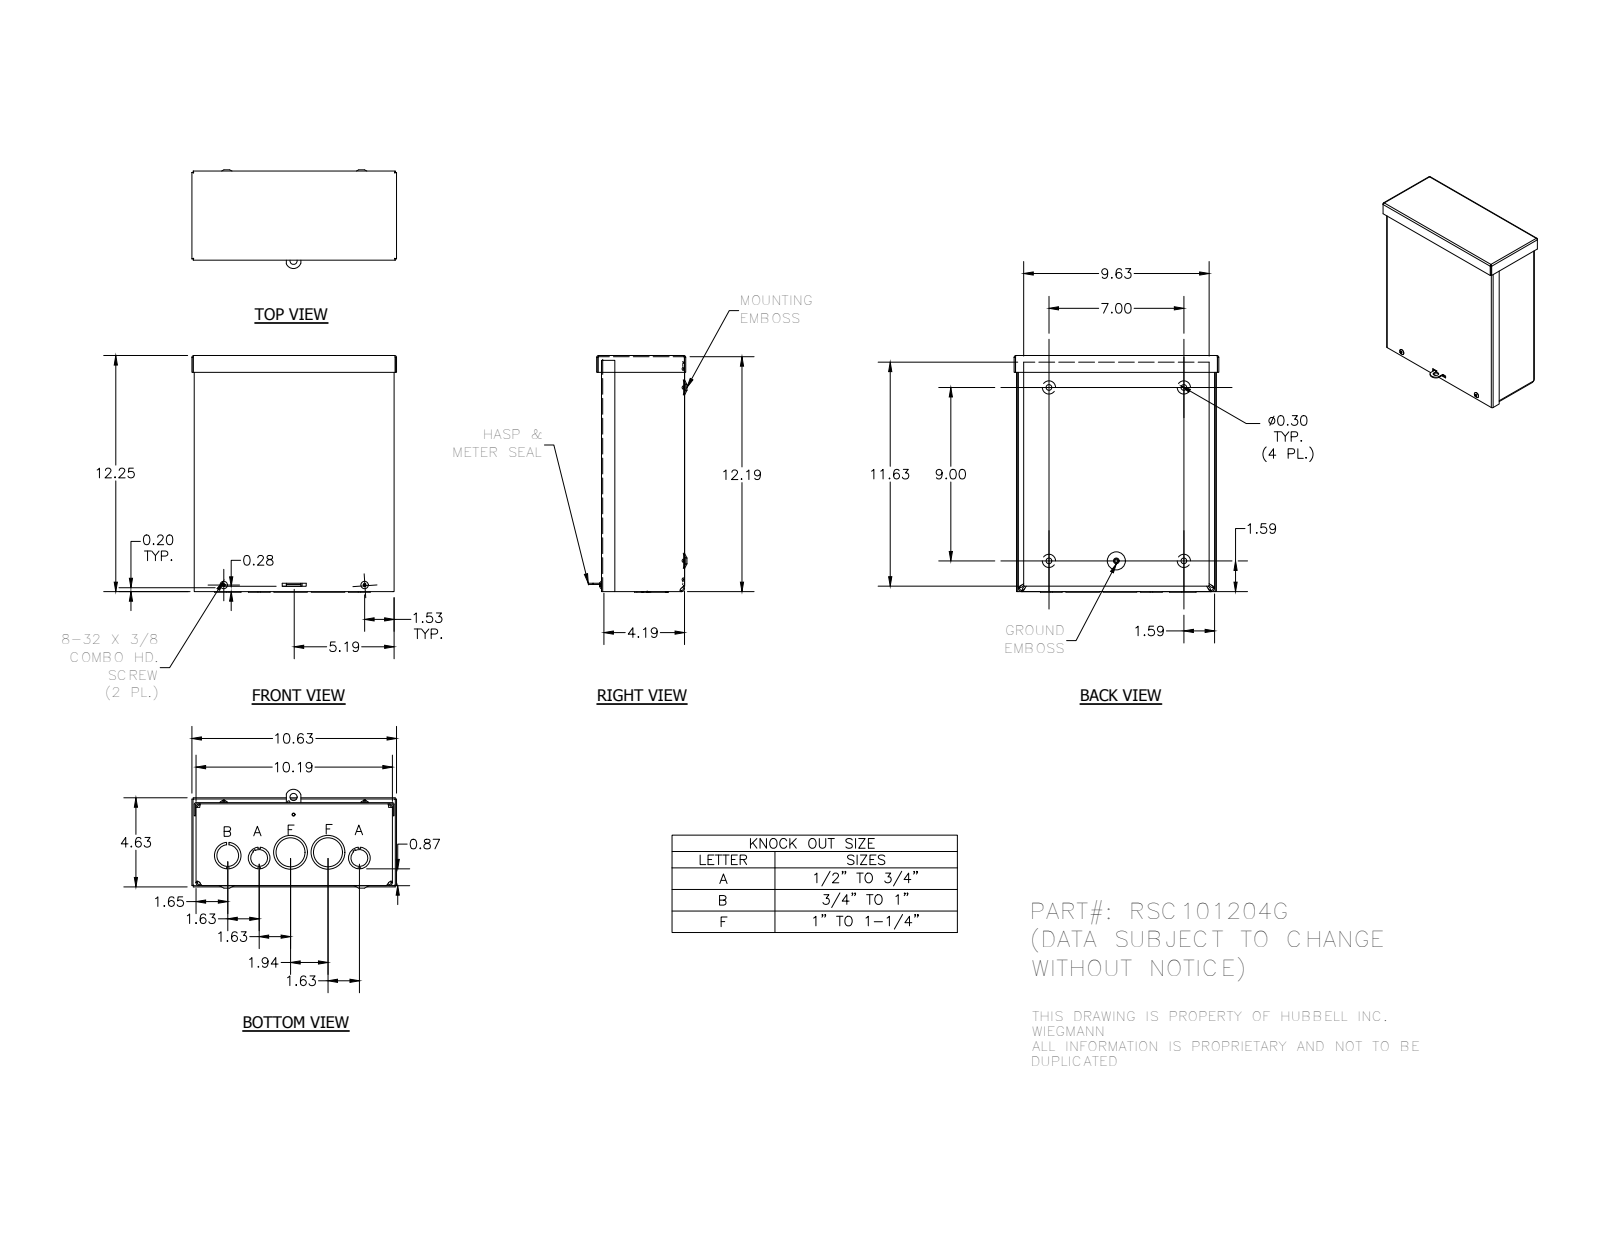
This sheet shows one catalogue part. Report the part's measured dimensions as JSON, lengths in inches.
{"part_name": "RSC101204G_WRAP; RSC1012G_LID; RSC1004G_CAP; 3183 (+4 more)", "step_written_by": "Autodesk Inventor 2014 (AUTOMOTIVE_DESIGN)", "units": "inches", "bodies": {"solids": 7, "faces": 518, "planar": 245, "cylindrical": 129, "other": 144}, "overall_size": [12.281, 10.625, 5.125], "volume_in3": 35.43, "surface_area_in2": 1160, "round_holes": [[0.3, 4], [0.313, 4], [1.125, 3], [0.125, 2], [0.148, 2], [0.875, 2], [1.5, 2], [1.75, 2], [0.156, 1], [0.165, 1], [0.375, 1], [1.375, 1]], "round_bosses_or_shafts": [[0.384, 2], [0.164, 2], [0.228, 1]], "partial_cylinders_radius": [[0.01, 10], [0.031, 8], [0.093, 8], [0.125, 8], [0.187, 8], [0.031, 4], [0.055, 4], [0.062, 4]], "face_to_face_distances": [0.062, 4.249, 4.187, 0.062, 0.063, 4.312, 4.25, 10.126, 0.124, 12.126], "hole_center_spacings": [1.072, 1.261, 1.656, 3.5, 3.582, 7, 7.313, 9]}
